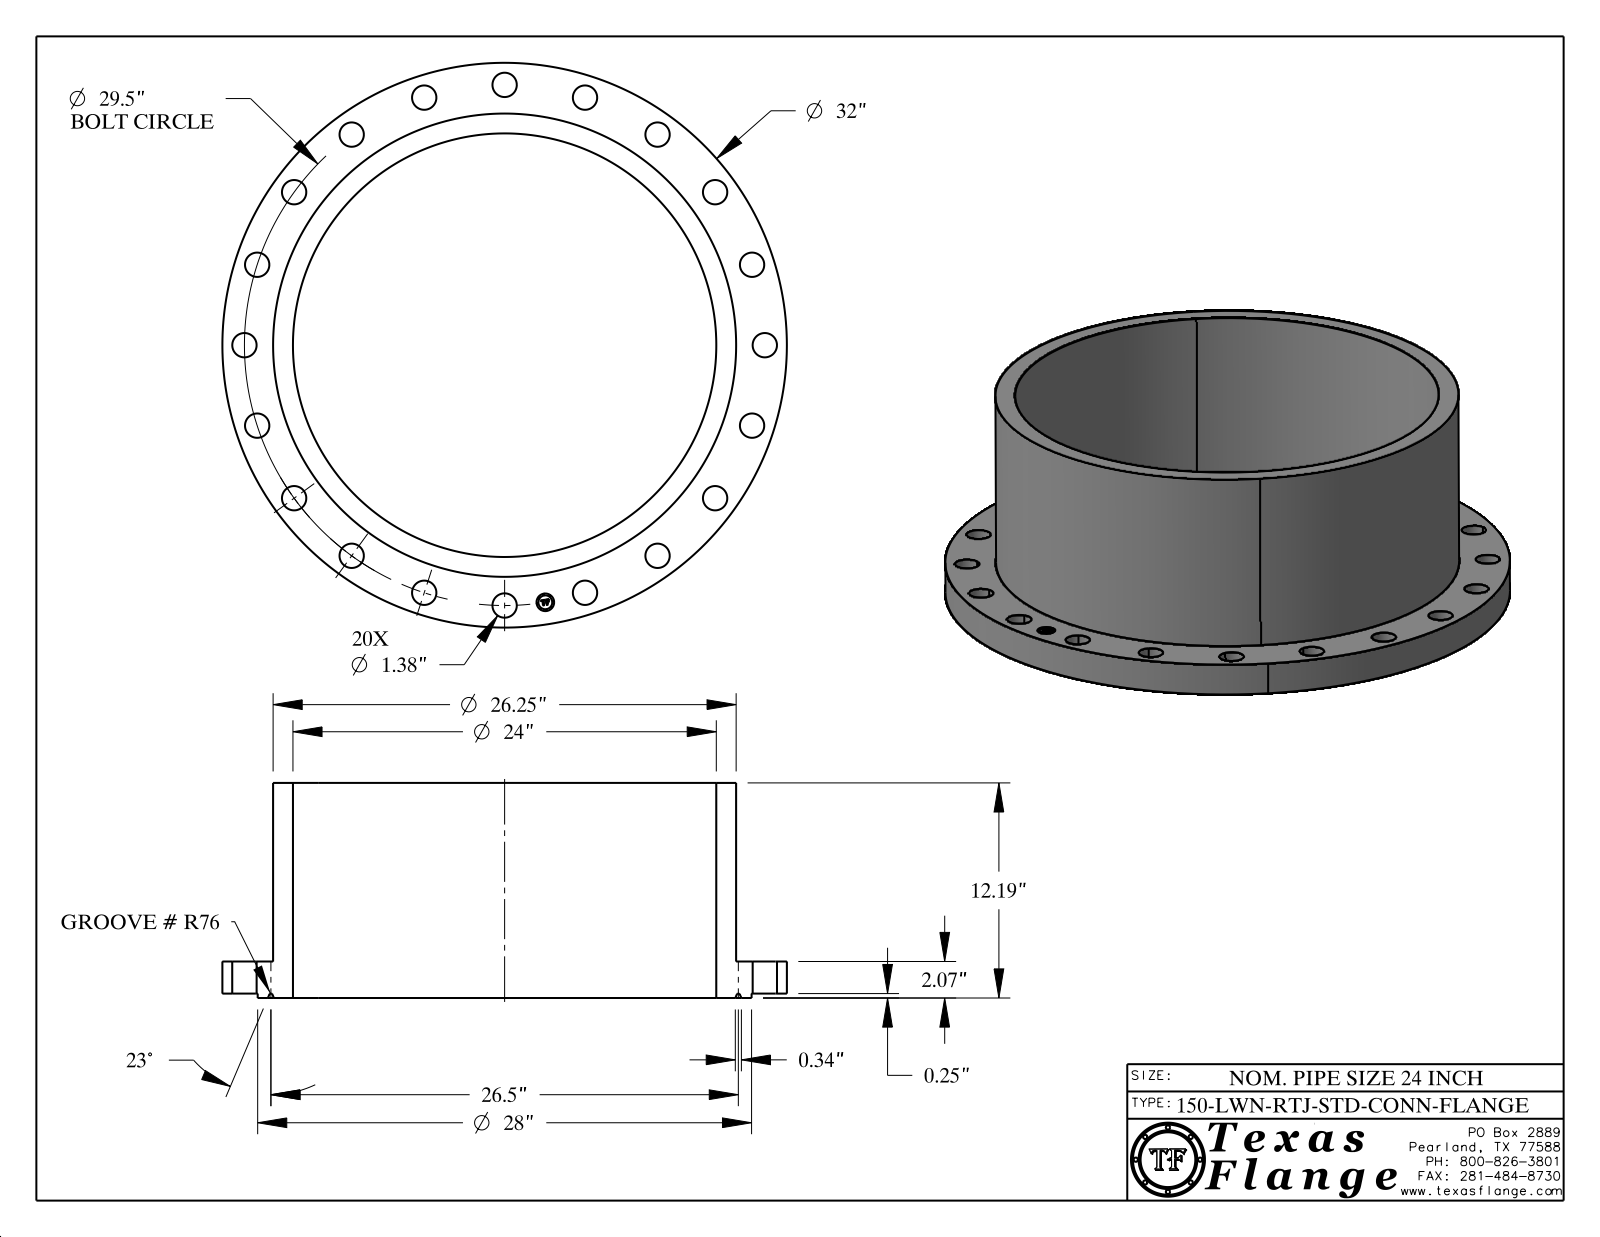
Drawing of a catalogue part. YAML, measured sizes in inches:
part_name: "24-150-LWN-RTJ-STD-CONN-FLANGE"
step_written_by: "CATIA V5 STEP AP214 (AUTOMOTIVE_DESIGN)"
units: inches
bodies: {solids: 1, faces: 447, planar: 371, cylindrical: 68, other: 8}
overall_size: [32, 32, 12.188]
volume: 1520
surface_area: 2786
round_holes:
  - {diameter: 1.38, count: 20}
  - {diameter: 1, count: 1}
  - {diameter: 24, count: 1}
round_bosses_or_shafts:
  - {diameter: 0.061, count: 8}
  - {diameter: 32, count: 1}
  - {diameter: 28, count: 1}
  - {diameter: 26.25, count: 1}
  - {diameter: 0.788, count: 1}
face_to_face_distances: [1.817, 0.25, 2.067, 12.187, 11.937, 10.12, 2.063, 1.813, 10.125, 0.298]
hole_center_spacings: [14.75, 29.137, 4.615, 17.34, 20.859, 23.866, 26.285, 9.116]
